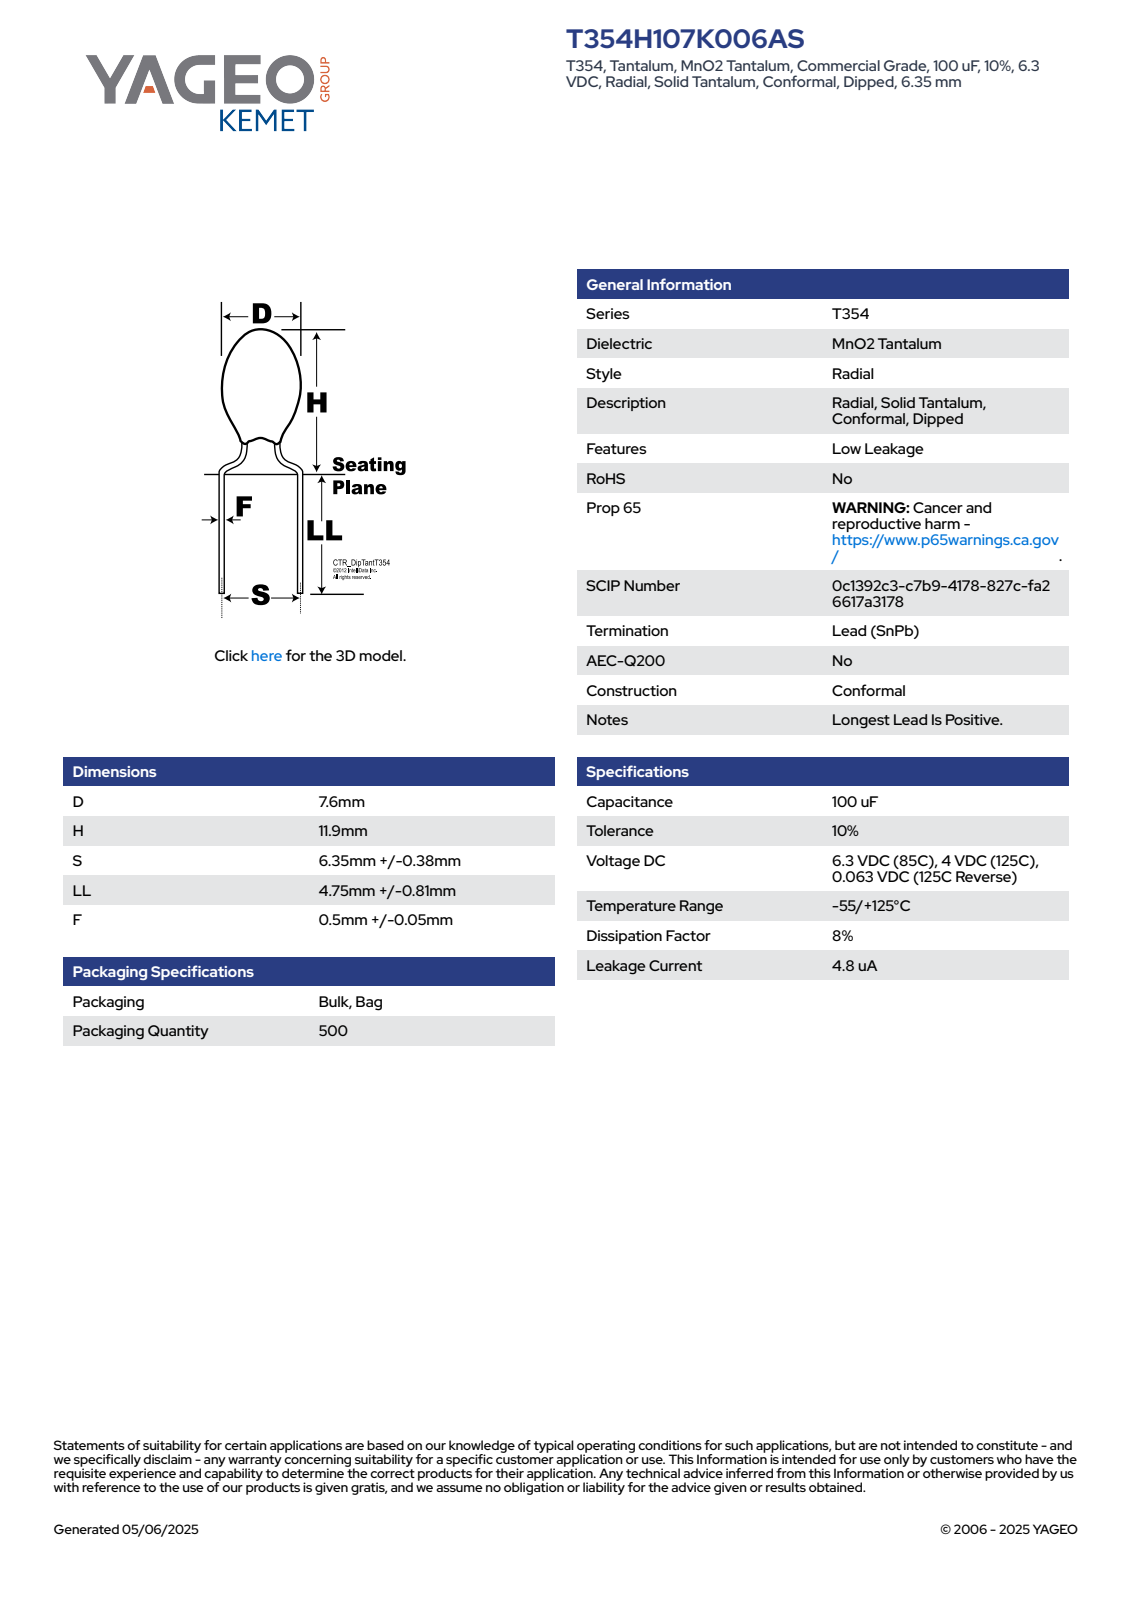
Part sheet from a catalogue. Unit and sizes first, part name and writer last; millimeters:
Units: millimetres
Overall size (bounding box): 17.46 × 7.6 × 7.6
Round bosses / shafts (diameter × count): ⌀0.55 ×2, ⌀7.6 ×1
Partial cylindrical surfaces — rounded edges, fillets, slot ends (radius × count): R3.79 ×1
Main face-to-face distances: 8.3, 9.16, 17.46, 14.5, 5.34, 2.96, 13.69, 4.53, 0.81, 3.77
Volume: 333 mm³ · Surface area: 272 mm²
Bodies: 1 solid, 81 faces (26 planar, 10 cylindrical, 45 other)
Part name (STEP PRODUCT): CTR_T354_D7.6H11.9S6.35LL5.56F0.55
STEP written by: SolidWorks 2014 (AUTOMOTIVE_DESIGN)
